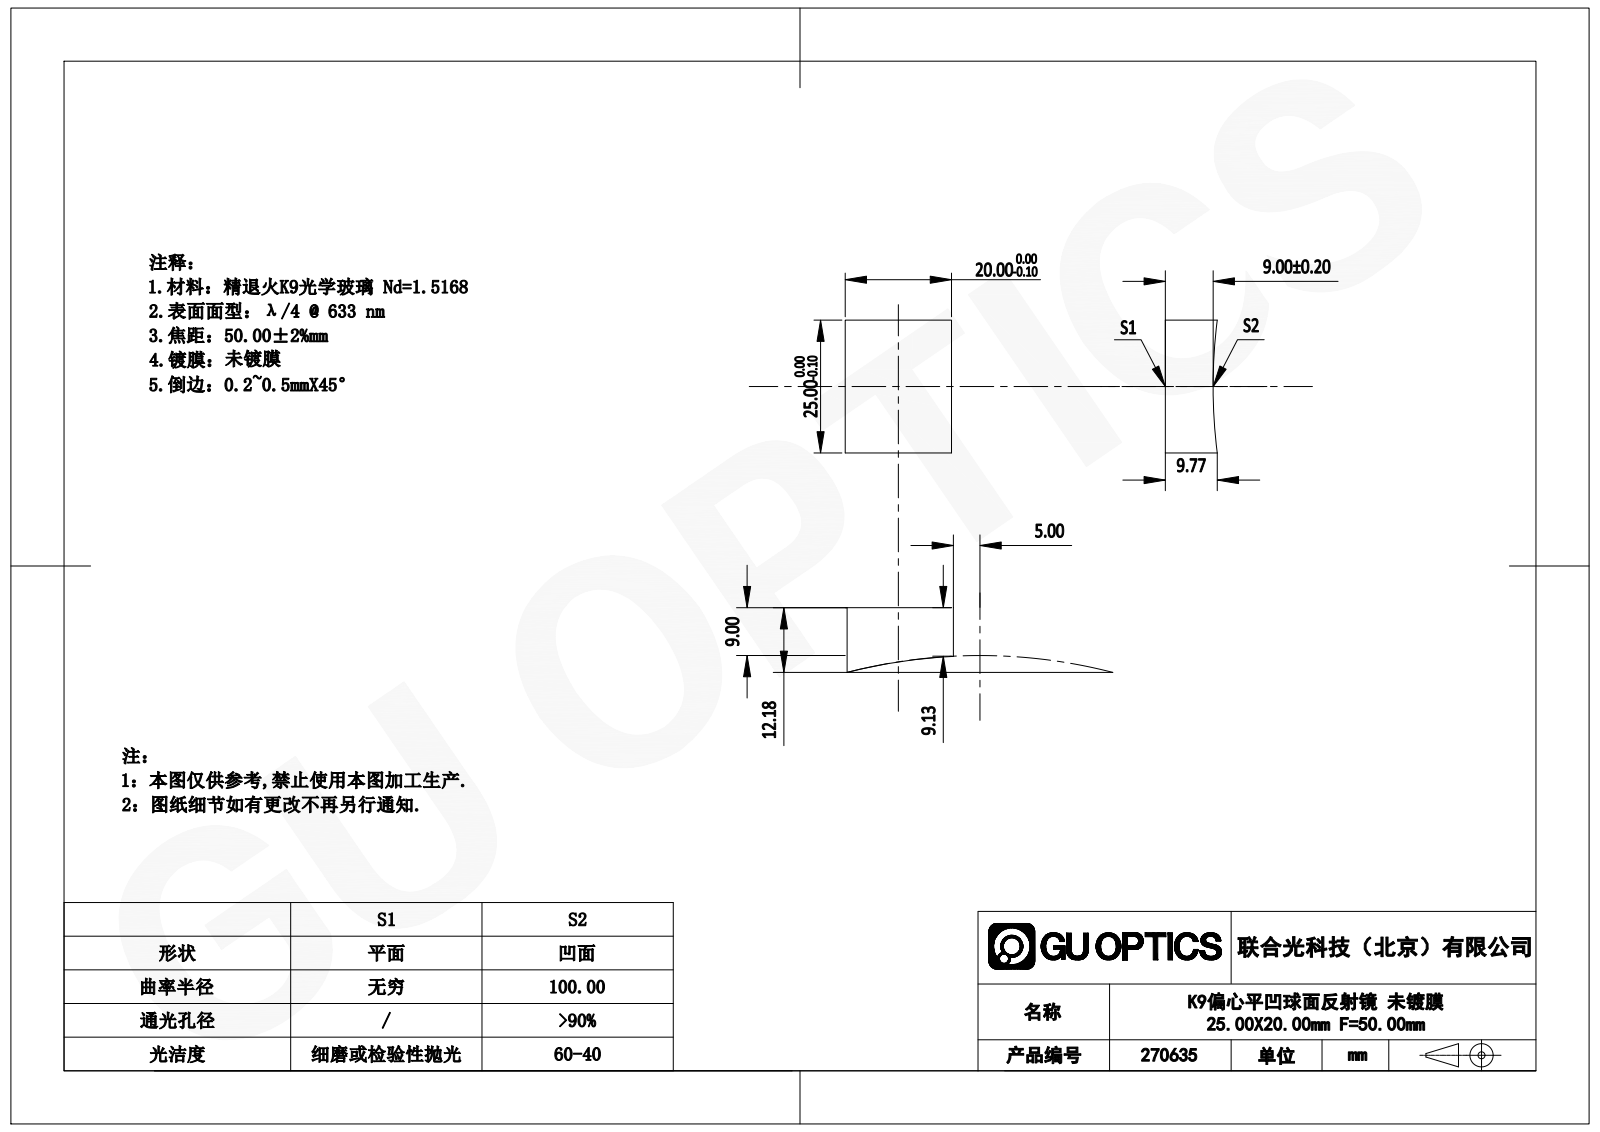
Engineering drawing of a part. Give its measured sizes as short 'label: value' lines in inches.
name: 270635
written by: SolidWorks 2020 (CONFIG_CONTROL_DESIGN)
unit: in
bodies: 1 solid, 7 faces (5 planar, 0 cylindrical, 2 other)
size: 0.984 × 0.787 × 0.511
volume: 0.322 in³; area: 3.097 in²
face distances: 0.787, 0.984
